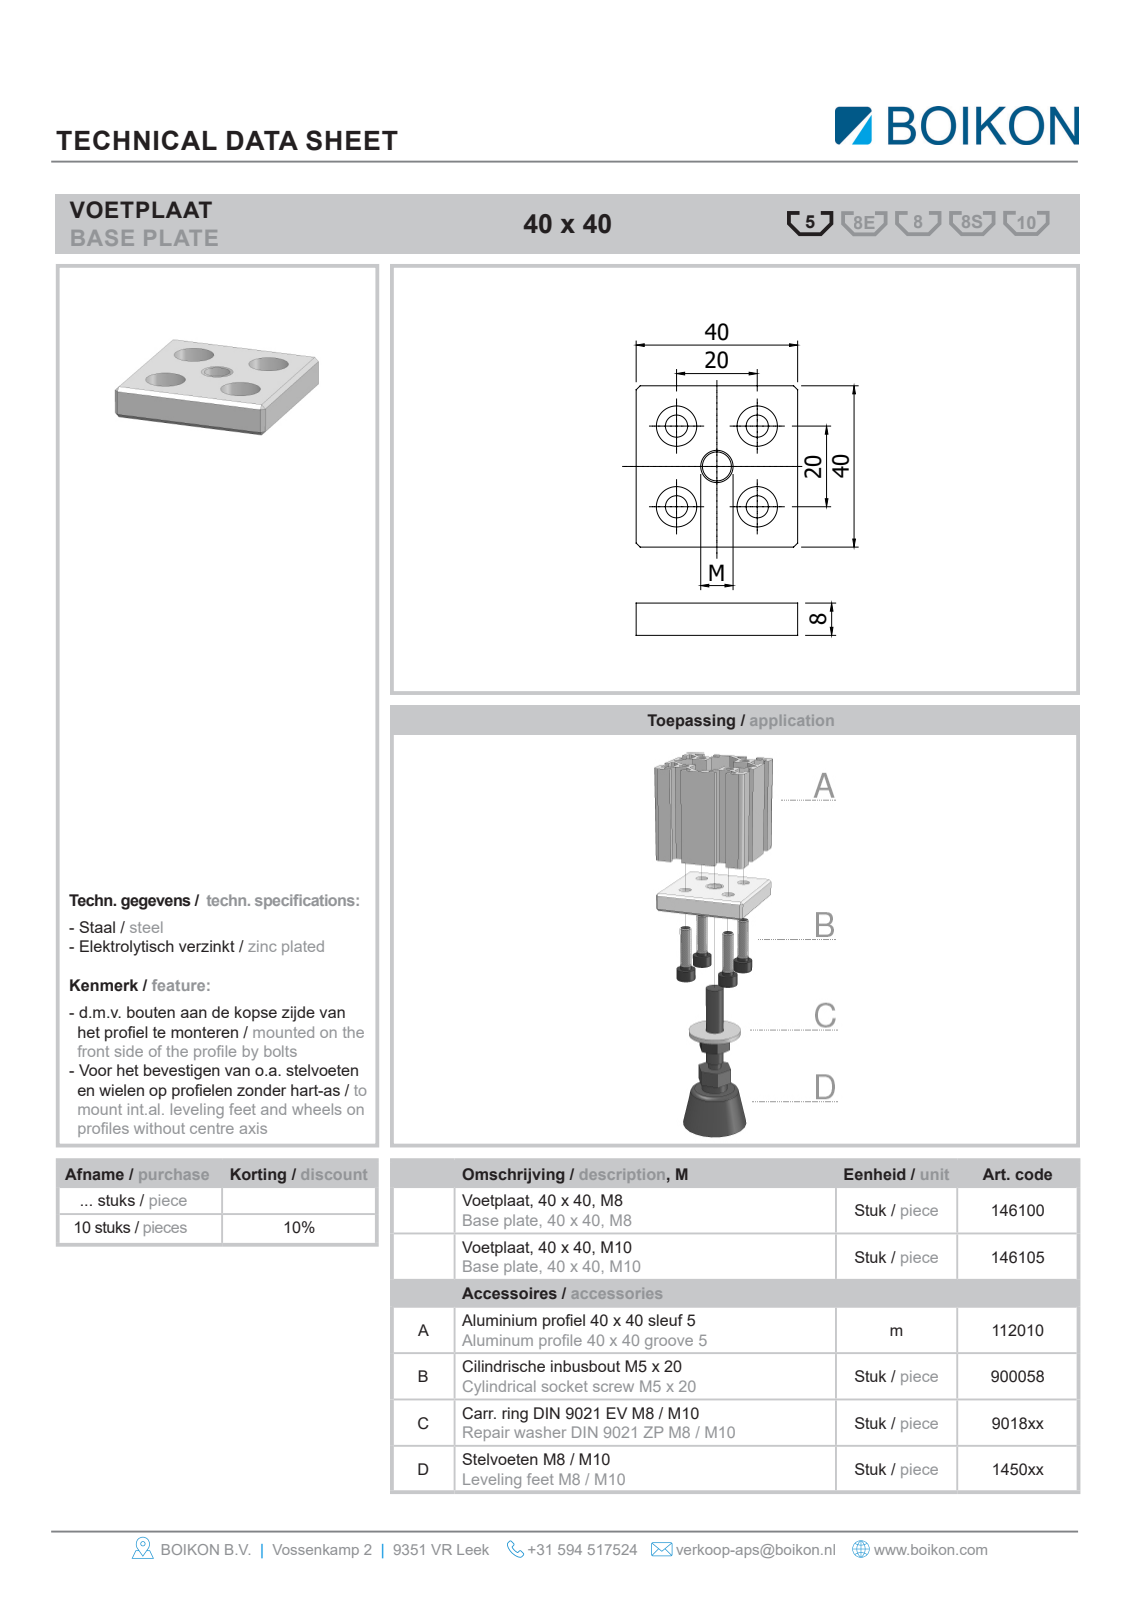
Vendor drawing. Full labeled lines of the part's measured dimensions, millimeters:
Part name (STEP PRODUCT): Root; 146105Voetplaat 40x40 M10BOIKON; 900058Cil. inbusbout DIN 912 EV M5 x 20BOIKON0
STEP written by: HiCAD 2013 1802.4 Build 509 (AUTOMOTIVE_DESIGN)
Units: millimetres
Bodies: 5 solids, 103 faces (70 planar, 21 cylindrical, 12 other)
Overall size (bounding box): 40 × 40 × 25.5
Volume: 12 246 mm³ · Surface area: 7 372 mm²
Round holes (diameter × count): ⌀10 ×5, ⌀5.5 ×4
Round bosses / shafts (diameter × count): ⌀8.5 ×4, ⌀5 ×4, ⌀4.02 ×4
Main face-to-face distances: 8, 40, 2.5, 5.5, 5, 7.5, 0.5, 20, 4, 17.5
Hole centre spacings: 14.14, 20, 28.28
